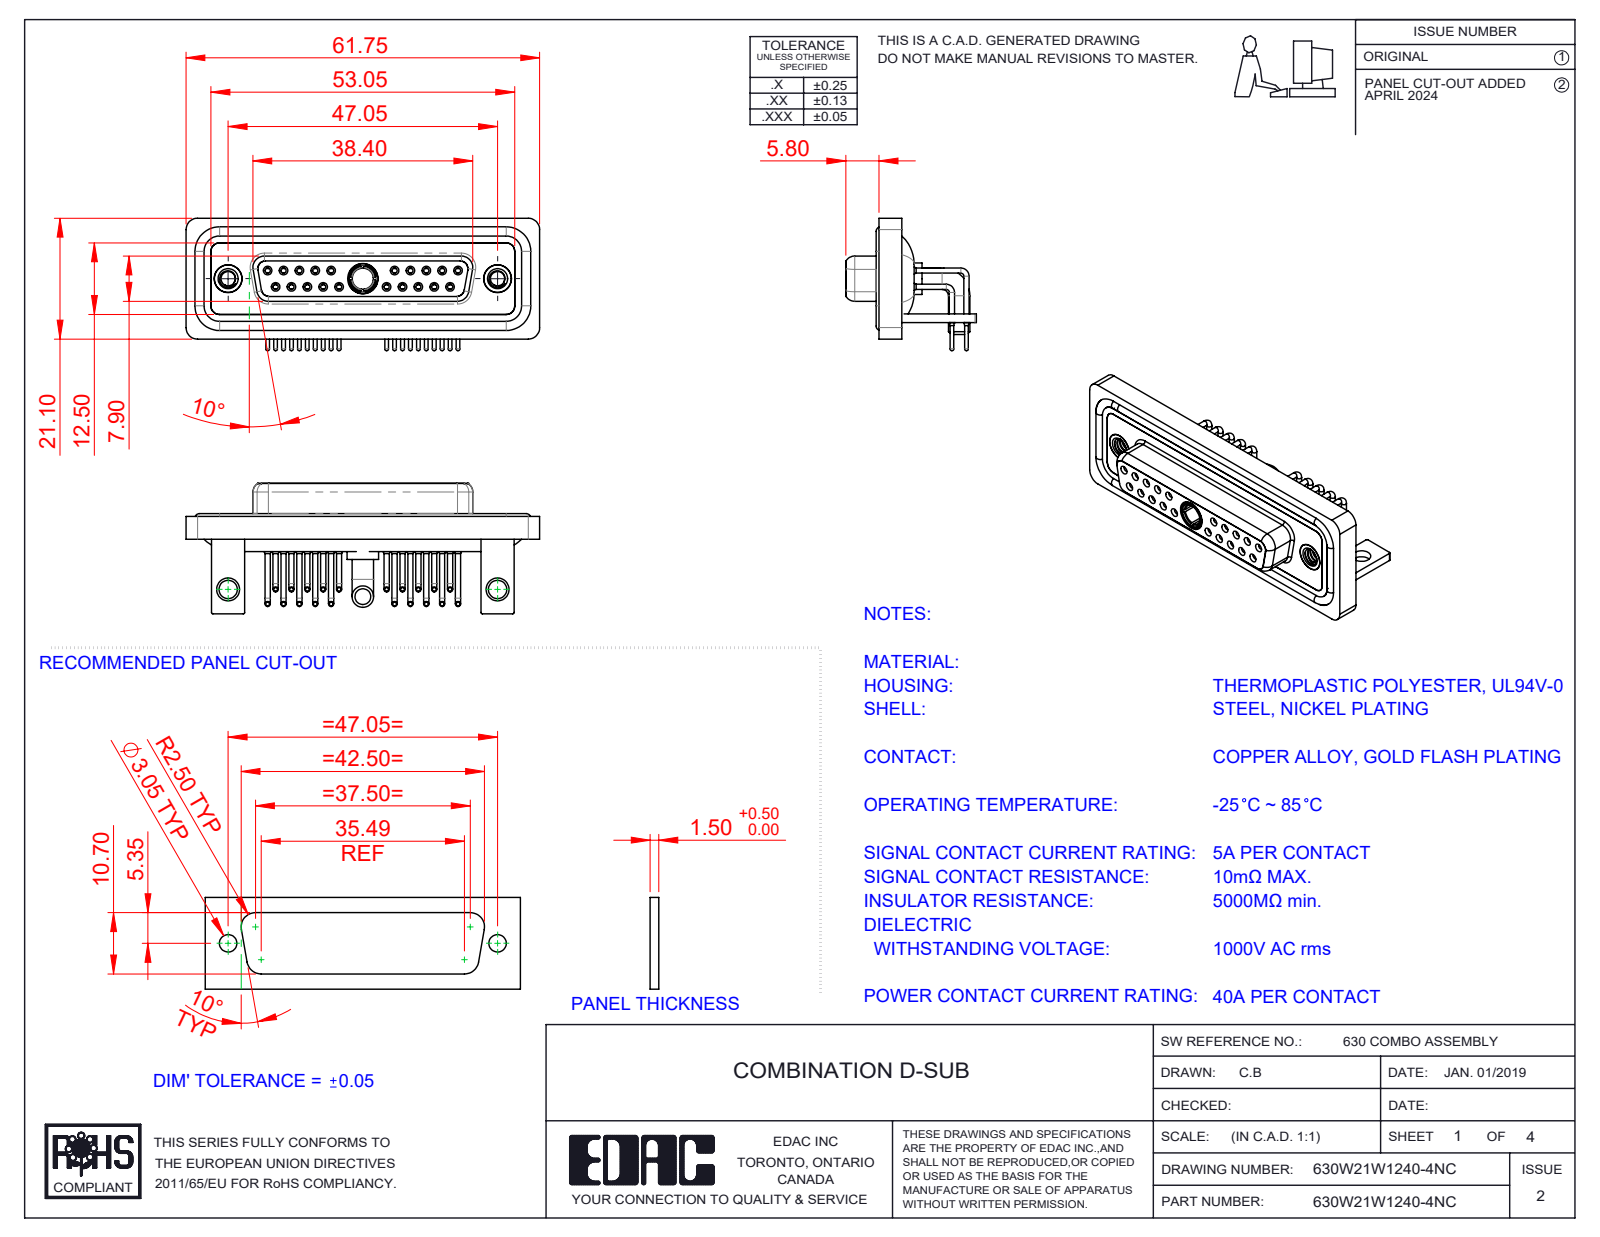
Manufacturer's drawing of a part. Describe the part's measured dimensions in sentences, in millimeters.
The part is named "Power Socket_40A RA; 630Combo Stabilizer Bracket_50 Contacts; 630Combo Contact Row 2_50 Contacts; 630Combo Shell Front_25 Contacts (+6 more)". Its 3-D file was written by "SolidWorks 2023 (CONFIG_CONTROL_DESIGN)". It is 31 solids with 1566 faces: 454 planar, 695 cylindrical and 417 other. Overall it measures 61.75 by 23.12 by 22.8 millimeters. Its volume is 8 938 cubic millimeters and its surface area 15 562 square millimeters. Round holes: 20 of diameter 0.9, 20 of diameter 1.1, 20 of diameter 1.5, 20 of diameter 2, 10 of diameter 1.6, 10 of diameter 1.7, 3 of diameter 4.85, 2 of diameter 2.5, 2 of diameter 3.2, 2 of diameter 4, 2 of diameter 4.05, 2 of diameter 5. Round bosses or shafts: 20 of diameter 0.9, 20 of diameter 0.65, 14 of diameter 1.6, 2 of diameter 4.95, 2 of diameter 4.8, 2 of diameter 3.75, 1 of diameter 5.5, 1 of diameter 5.2. Partial cylindrical surfaces (rounded edges, fillets, slot ends): 19 of radius 2, 18 of radius 1.5, 16 of radius 0.25, 8 of radius 1.35, 8 of radius 1.6, 5 of radius 0.5, 4 of radius 0.6, 4 of radius 0.65. The main face-to-face distances are 0.4, 1.8, 2.9, 3.7, 1.5, 4.1, 1.1, 1.4, 1.6, 2.5. The hole center spacings are 3.16, 2.77, 5.54, 8.31, 5.04, 19.39, 20.97, 22.16.
